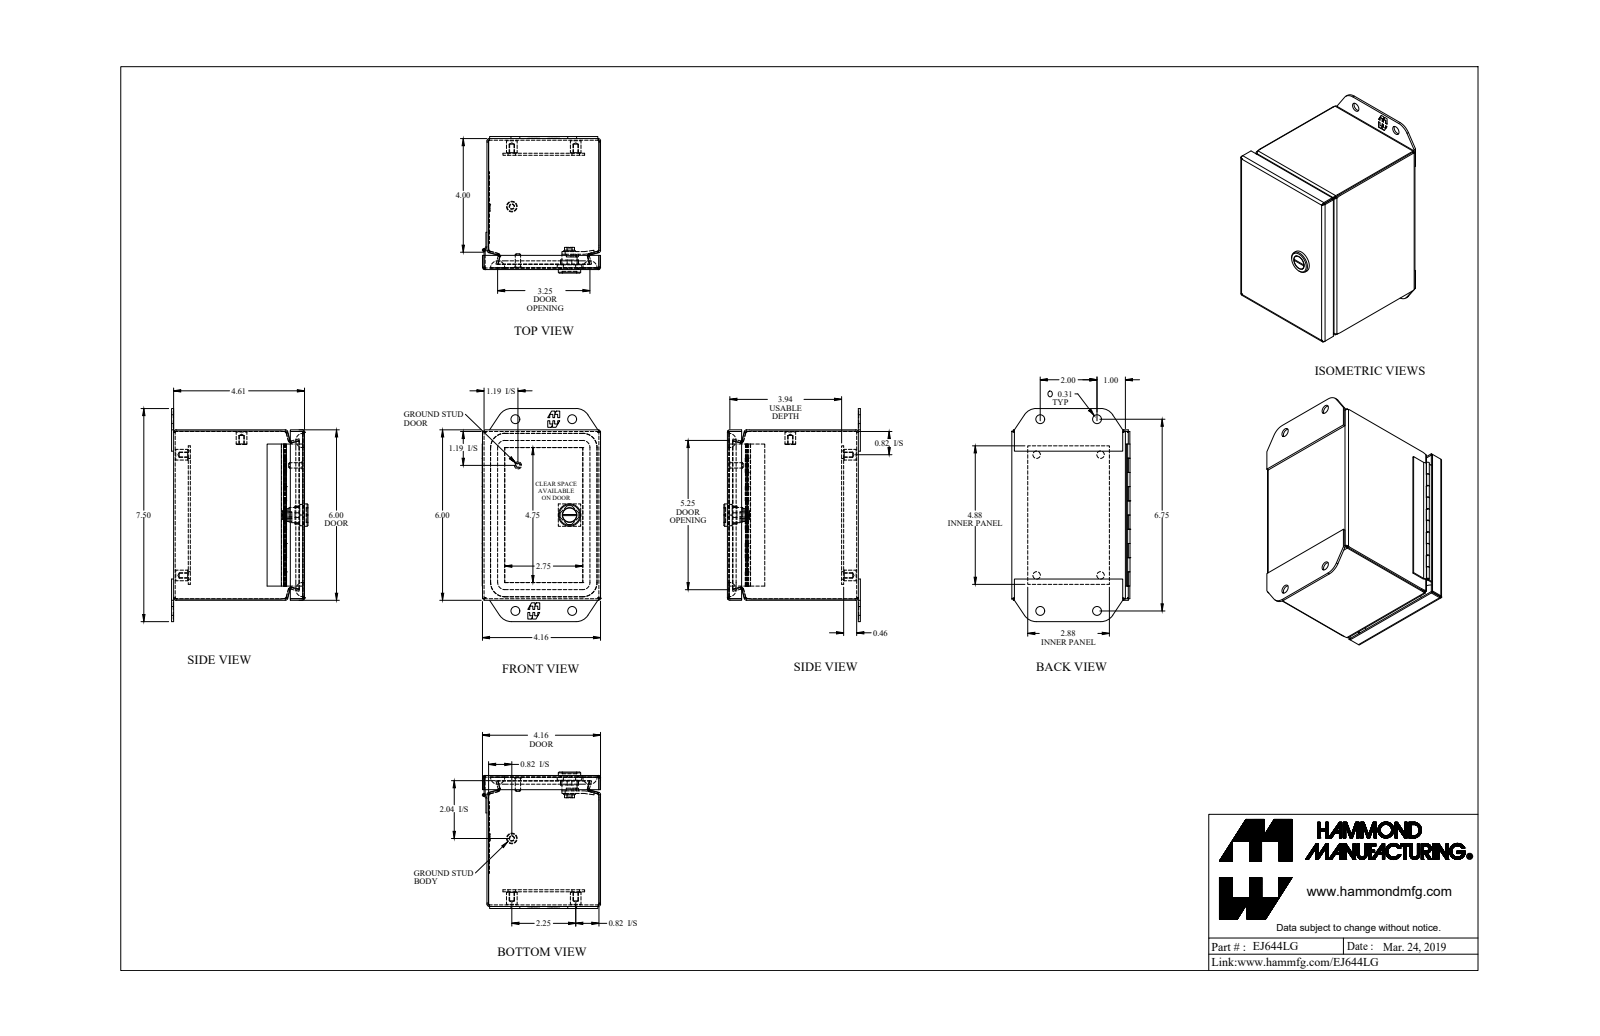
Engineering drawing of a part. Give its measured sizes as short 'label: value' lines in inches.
name: EJ644LG_Default
written by: SolidWorks 2019 (CONFIG_CONTROL_DESIGN)
unit: in
bodies: 16 solids, 611 faces (345 planar, 174 cylindrical, 92 other)
size: 7.5 × 4.805 × 4.165
volume: 12.43 in³; area: 410.6 in²
holes: 5× ⌀0.156, 4× ⌀0.265, 4× ⌀0.313, 1× ⌀0.05, 1× ⌀0.516
bosses: 5× ⌀0.375, 1× ⌀0.788, 1× ⌀0.535, 1× ⌀0.496, 1× ⌀0.435, 1× ⌀0.25, 1× ⌀0.188, 1× ⌀0.1
rounds: 16× R0.029, 16× R0.086, 10× R0.281, 4× R0.25, 4× R0.499, 4× R0.5, 2× R0.06, 2× R0.539
face distances: 0.057, 4.554, 3.943, 5.943, 0.072, 0.589, 3.886, 4.611, 4, 4.497
hole spacings: 1.256, 5.501, 2, 2.136, 2.25, 2.465, 2.466, 2.94
